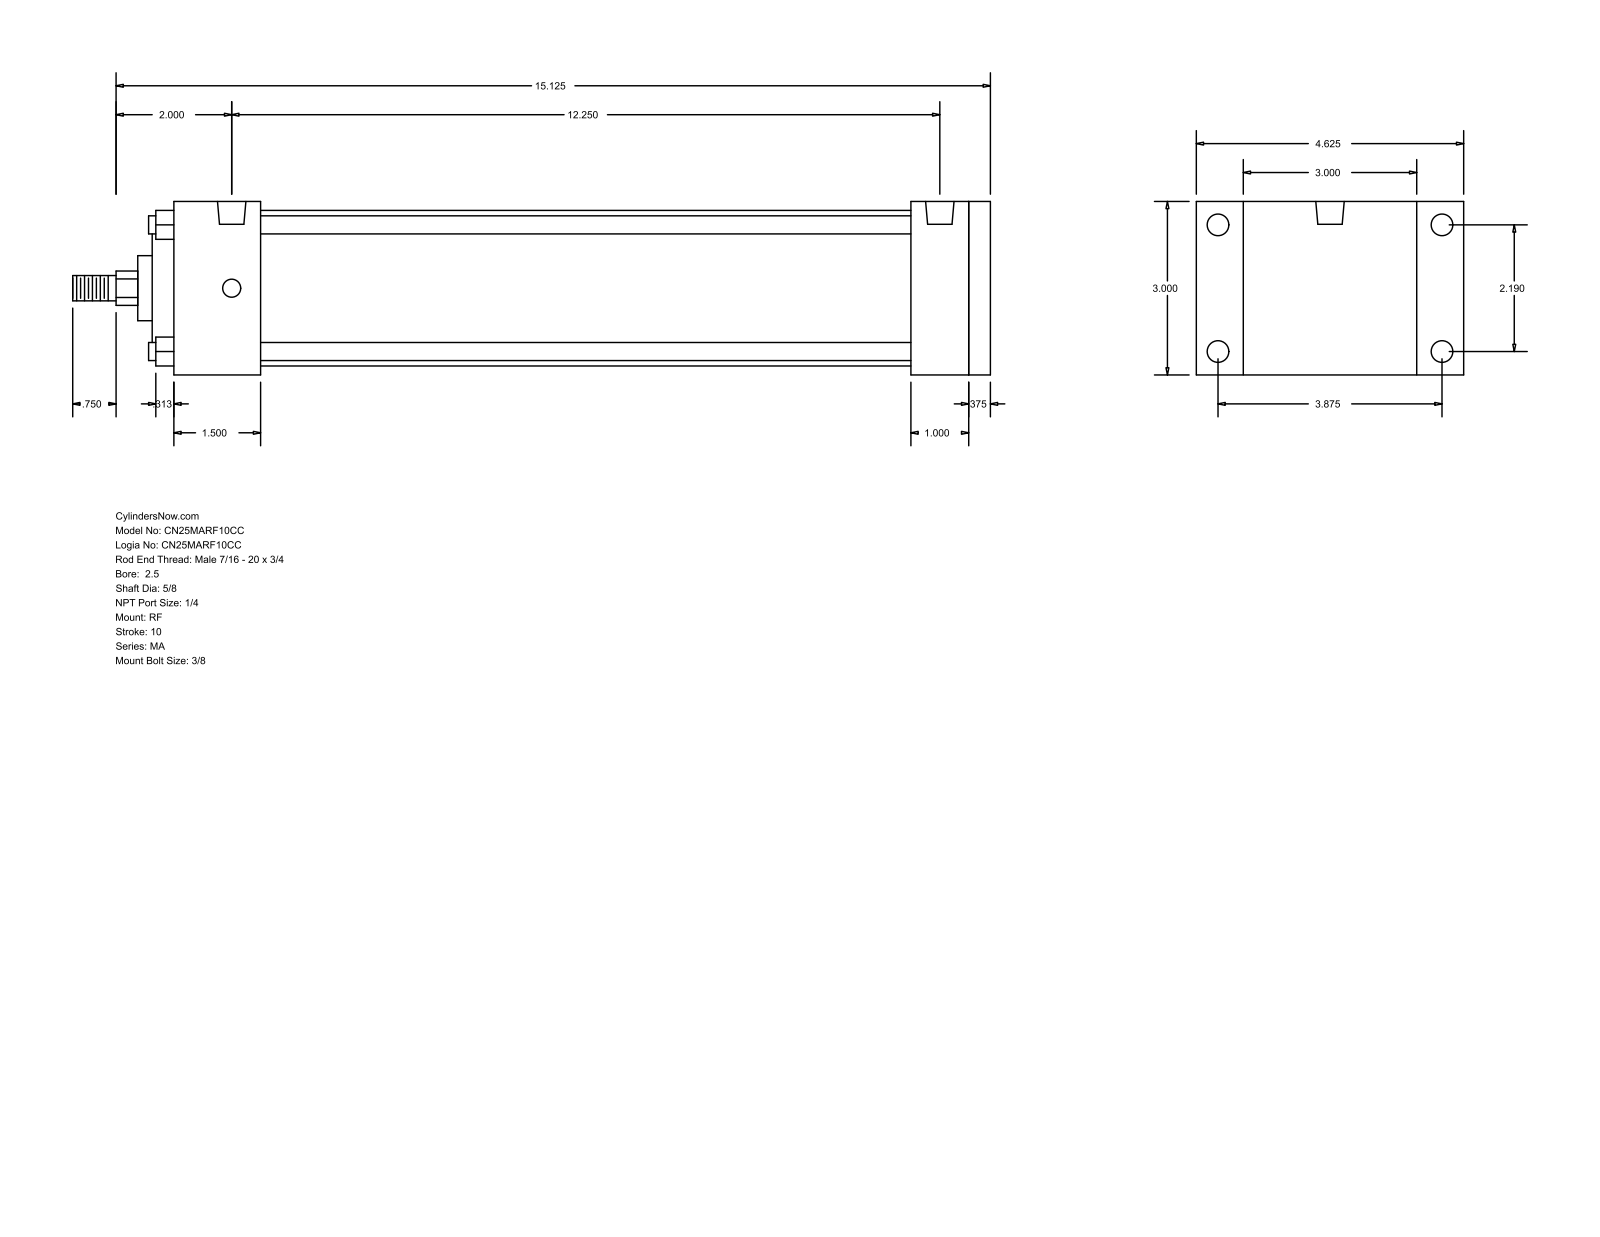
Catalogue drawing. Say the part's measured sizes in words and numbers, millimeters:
The part is named "MA_RF__0250_0.625". Its 3-D file was written by "GSSL Pune (CONFIG_CONTROL_DESIGN)". It is 0 solids with 94 faces: 65 planar, 29 cylindrical and 0 other. Overall it measures 403.23 by 117.47 by 76.2 millimeters. Round holes: 4 of diameter 7.94, 4 of diameter 9.53, 2 of diameter 12.49. Round bosses or shafts: 4 of diameter 7.94, 1 of diameter 68.33, 1 of diameter 50.8, 1 of diameter 28.57, 1 of diameter 15.88, 1 of diameter 11.11. Partial cylindrical surfaces (rounded edges, fillets, slot ends): 1 of radius 7.54. The main face-to-face distances are 76.2, 358.78, 9.53, 349.25, 25.4, 34.93, 38.1, 323.85, 285.75, 311.15. The hole center spacings are 55.62, 98.42, 113.05, 311.15.
